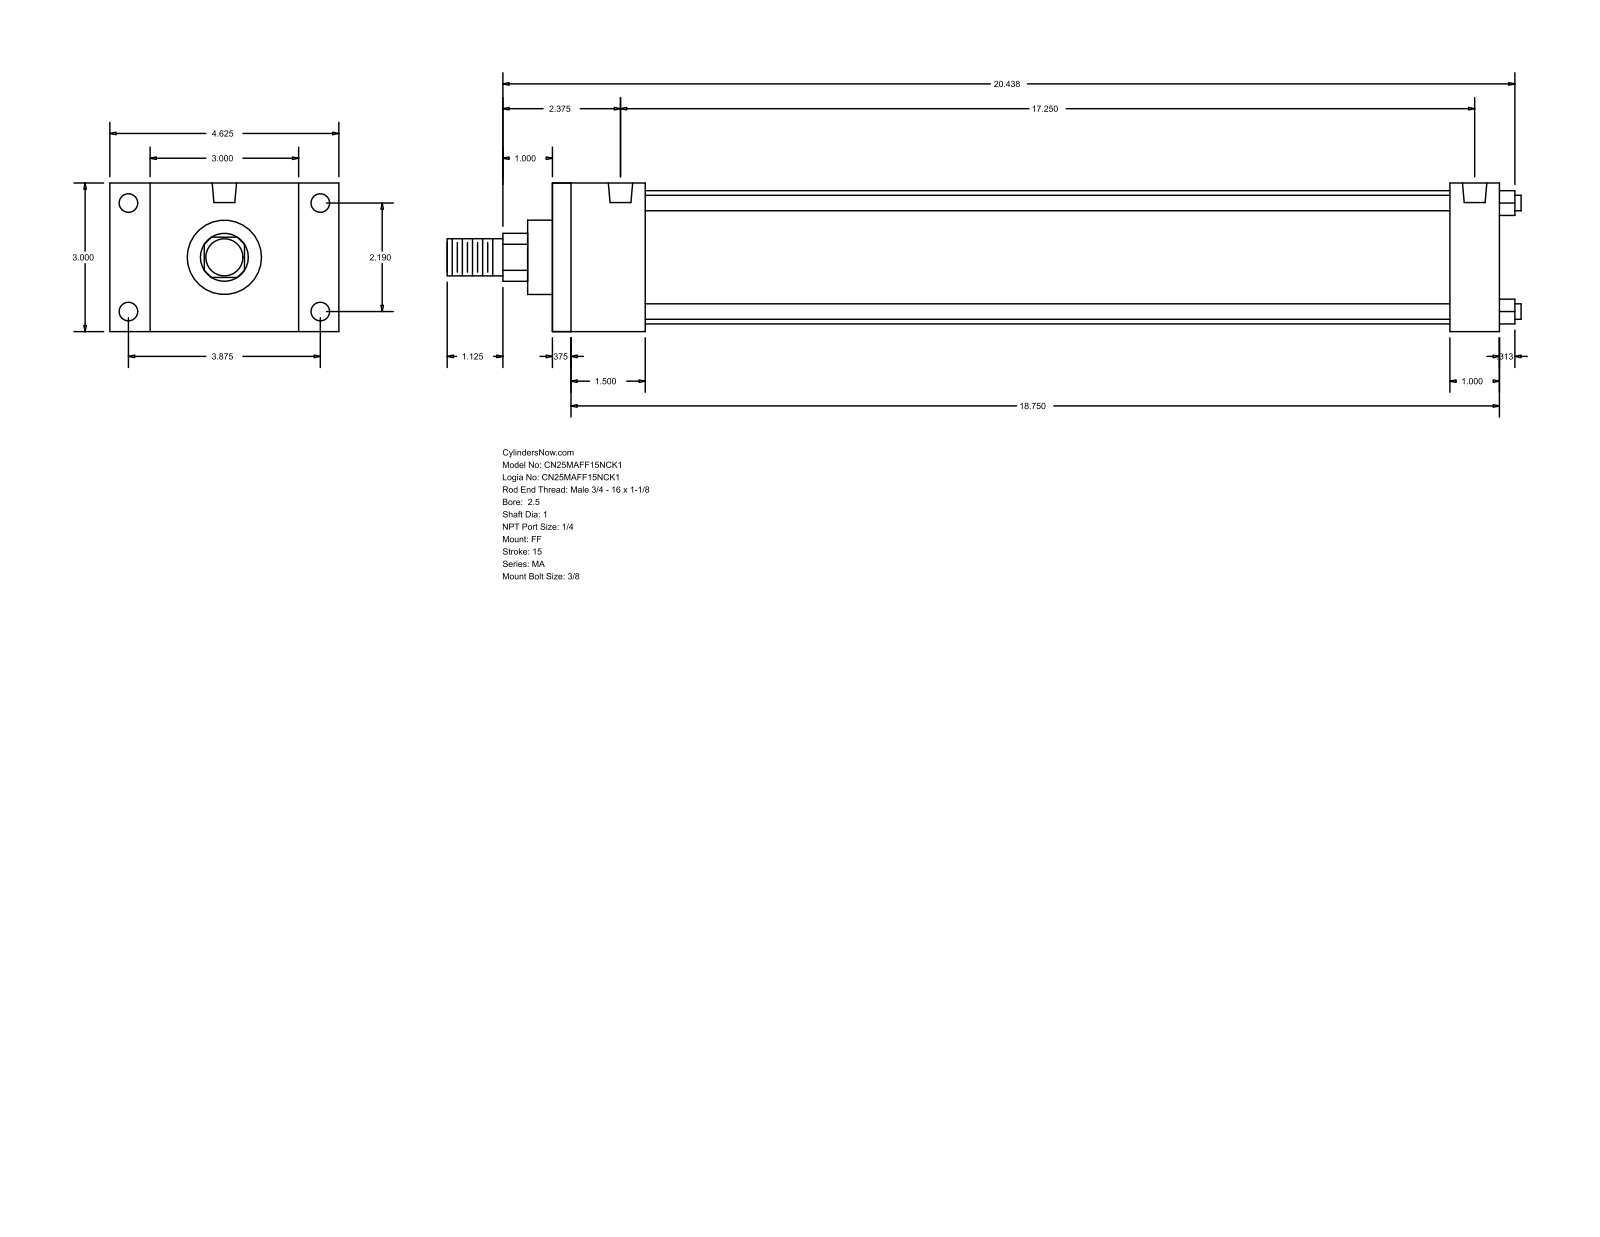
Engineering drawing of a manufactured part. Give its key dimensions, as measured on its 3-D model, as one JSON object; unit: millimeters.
{"part_name": "MA_FF__0250_1", "step_written_by": "GSSL Pune (CONFIG_CONTROL_DESIGN)", "units": "millimeters", "bodies": {"solids": 0, "faces": 92, "planar": 64, "cylindrical": 28, "other": 0}, "overall_size": [550.86, 117.47, 76.2], "round_holes": [[7.94, 4], [9.53, 4], [12.49, 2]], "round_bosses_or_shafts": [[7.94, 4], [68.33, 1], [38.1, 1], [25.4, 1], [19.05, 1]], "partial_cylinders_radius": [[12.29, 1]], "face_to_face_distances": [76.2, 485.78, 9.52, 476.26, 47.63, 460.37, 38.11, 450.85, 412.74, 438.15], "hole_center_spacings": [55.62, 98.42, 113.05, 438.15]}
